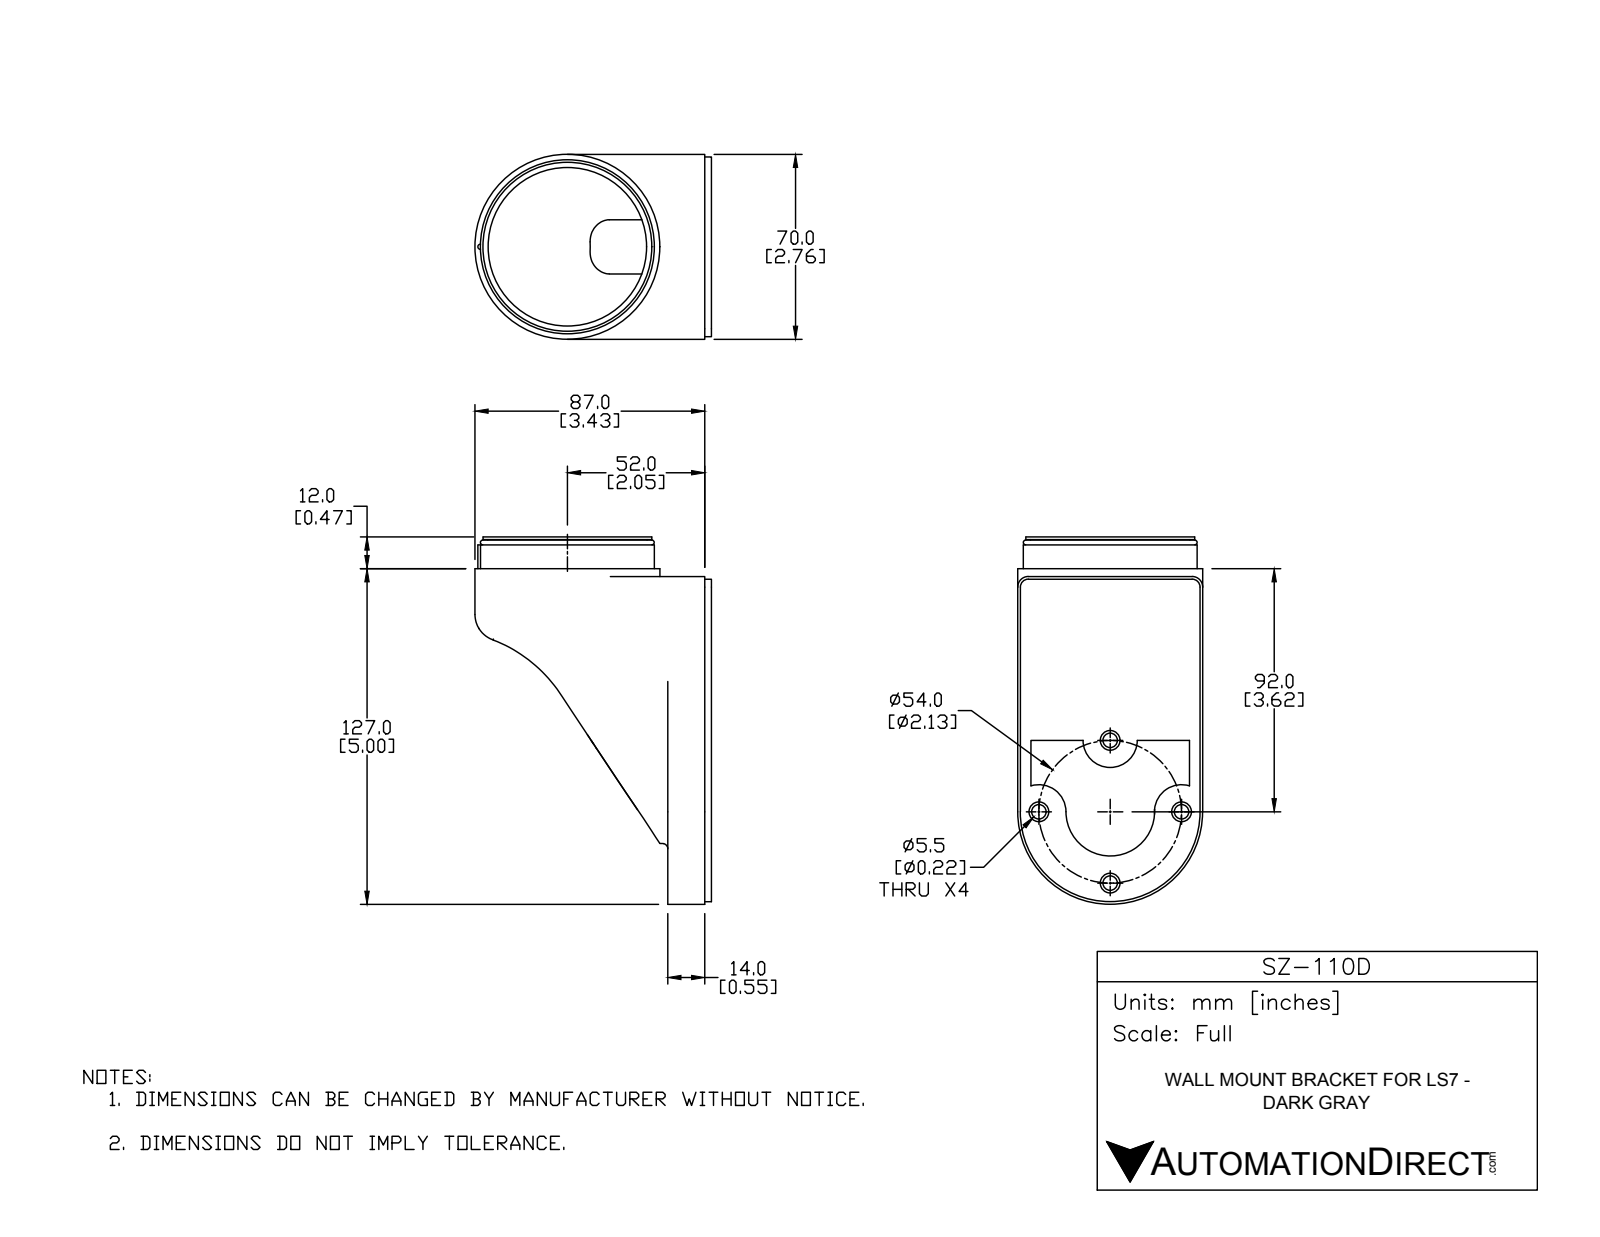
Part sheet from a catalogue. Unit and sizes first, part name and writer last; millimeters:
Units: millimetres
Overall size (bounding box): 139 × 89.5 × 71.99
Round holes (diameter × count): ⌀5.5 ×4, ⌀7.5 ×4, ⌀10.5 ×4, ⌀60 ×1
Round bosses / shafts (diameter × count): ⌀70 ×1, ⌀65.8 ×1, ⌀63.9 ×1, ⌀60.3 ×1, ⌀20.5 ×1
Partial cylindrical surfaces — rounded edges, fillets, slot ends (radius × count): R10.25 ×3, R3 ×2, R4 ×2, R1 ×1, R2 ×1, R7 ×1, R16.78 ×1, R30 ×1
Main face-to-face distances: 2.5, 5, 65, 14, 16.5, 70, 60, 9, 3, 11.5
Hole centre spacings: 38.18, 54
Volume: 133 500 mm³ · Surface area: 68 273 mm²
Bodies: 3 solids, 114 faces (28 planar, 57 cylindrical, 29 other)
Part name (STEP PRODUCT): SZ-110D
STEP written by: SolidWorks 2016 (AUTOMOTIVE_DESIGN)
